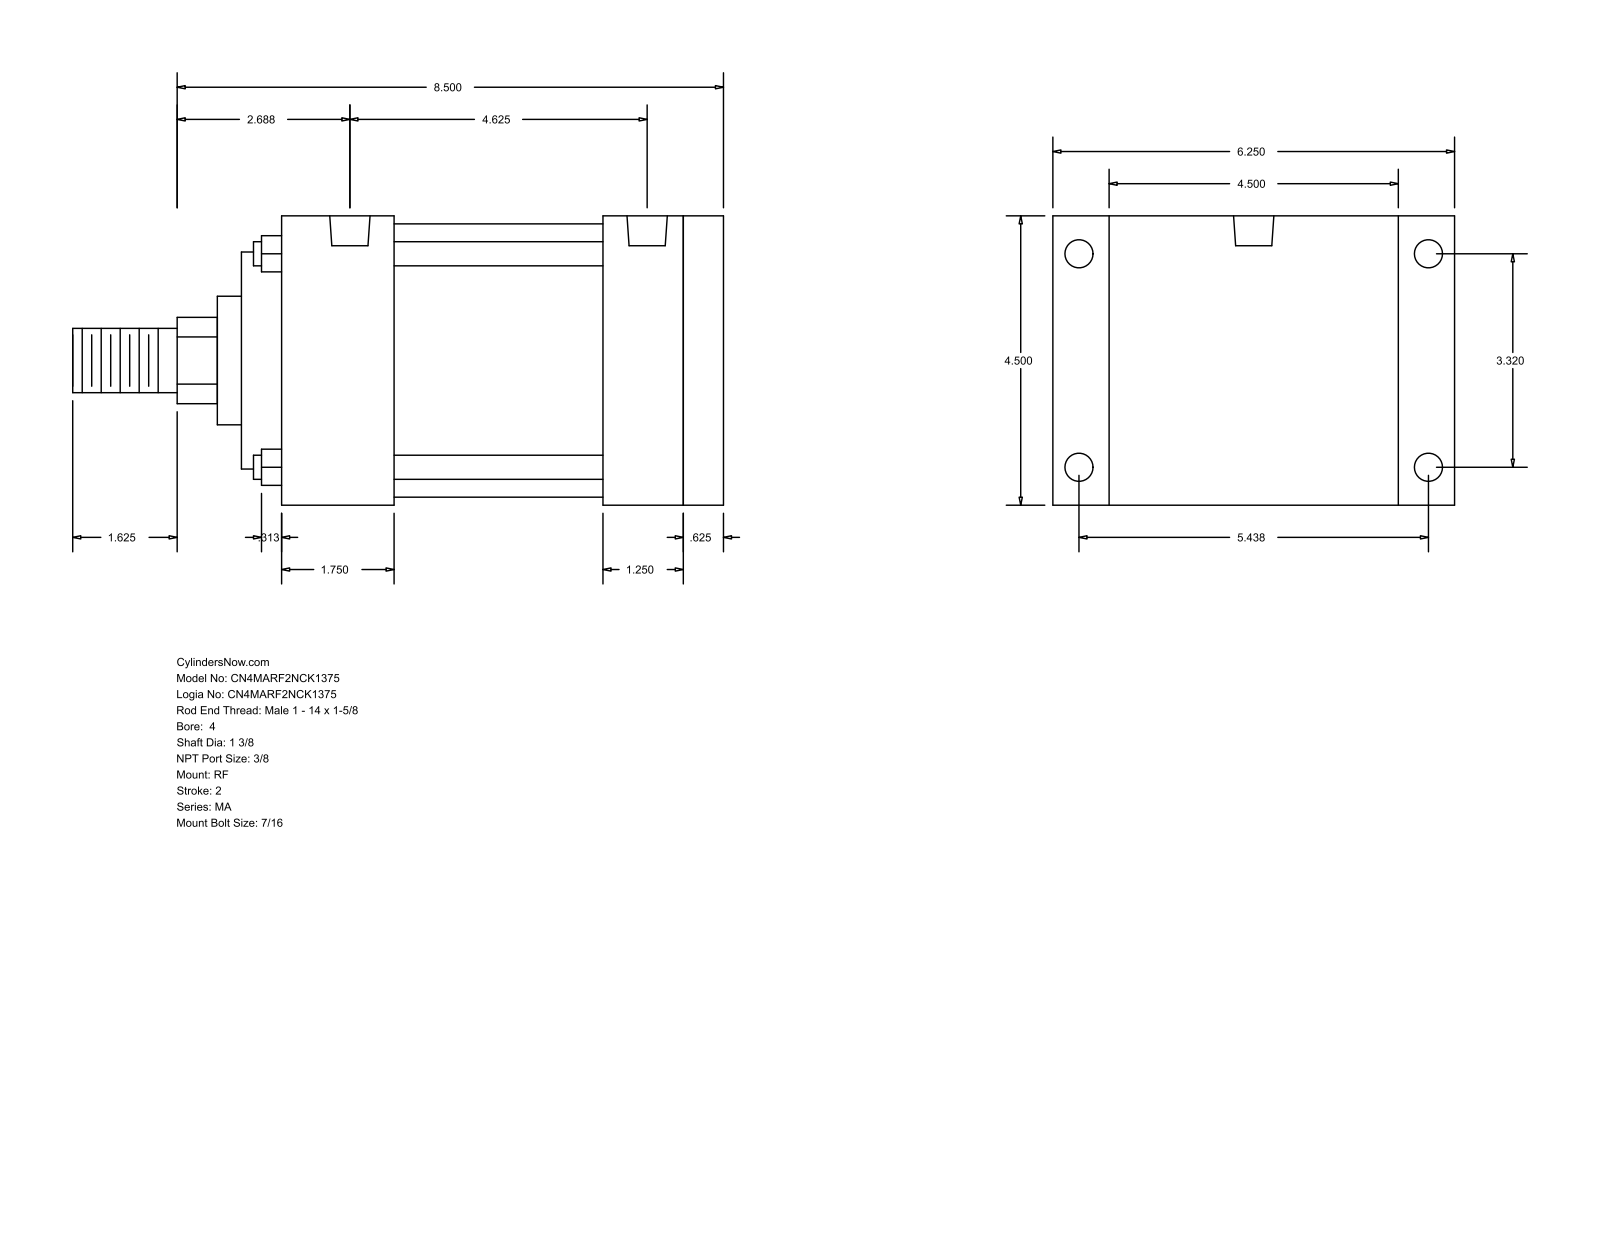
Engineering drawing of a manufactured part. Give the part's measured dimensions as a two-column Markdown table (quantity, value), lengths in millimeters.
| quantity | value |
| --- | --- |
| part name | MA_RF__0400_1.375 |
| STEP written by | GSSL Pune (CONFIG_CONTROL_DESIGN) |
| units | millimeters |
| bodies | 0 solids, 94 faces (65 planar, 29 cylindrical, 0 other) |
| overall size | 257.18 × 158.75 × 114.3 |
| round holes (diameter × count) | 11.11 × 8, 15.93 × 2 |
| round bosses / shafts (diameter × count) | 9.53 × 4, 107.95 × 1, 85.72 × 1, 50.8 × 1, 34.92 × 1, 25.4 × 1 |
| partial cylindrical surfaces (radius × count) | 17.06 × 1 |
| main face-to-face distances | 114.3, 174.63, 15.87, 158.76, 190.5, 22.23, 136.53, 142.88, 127.01, 31.75 |
| hole center spacings | 4.77, 84.32, 107.94, 112.71, 138.12, 161.82, 117.48 |
